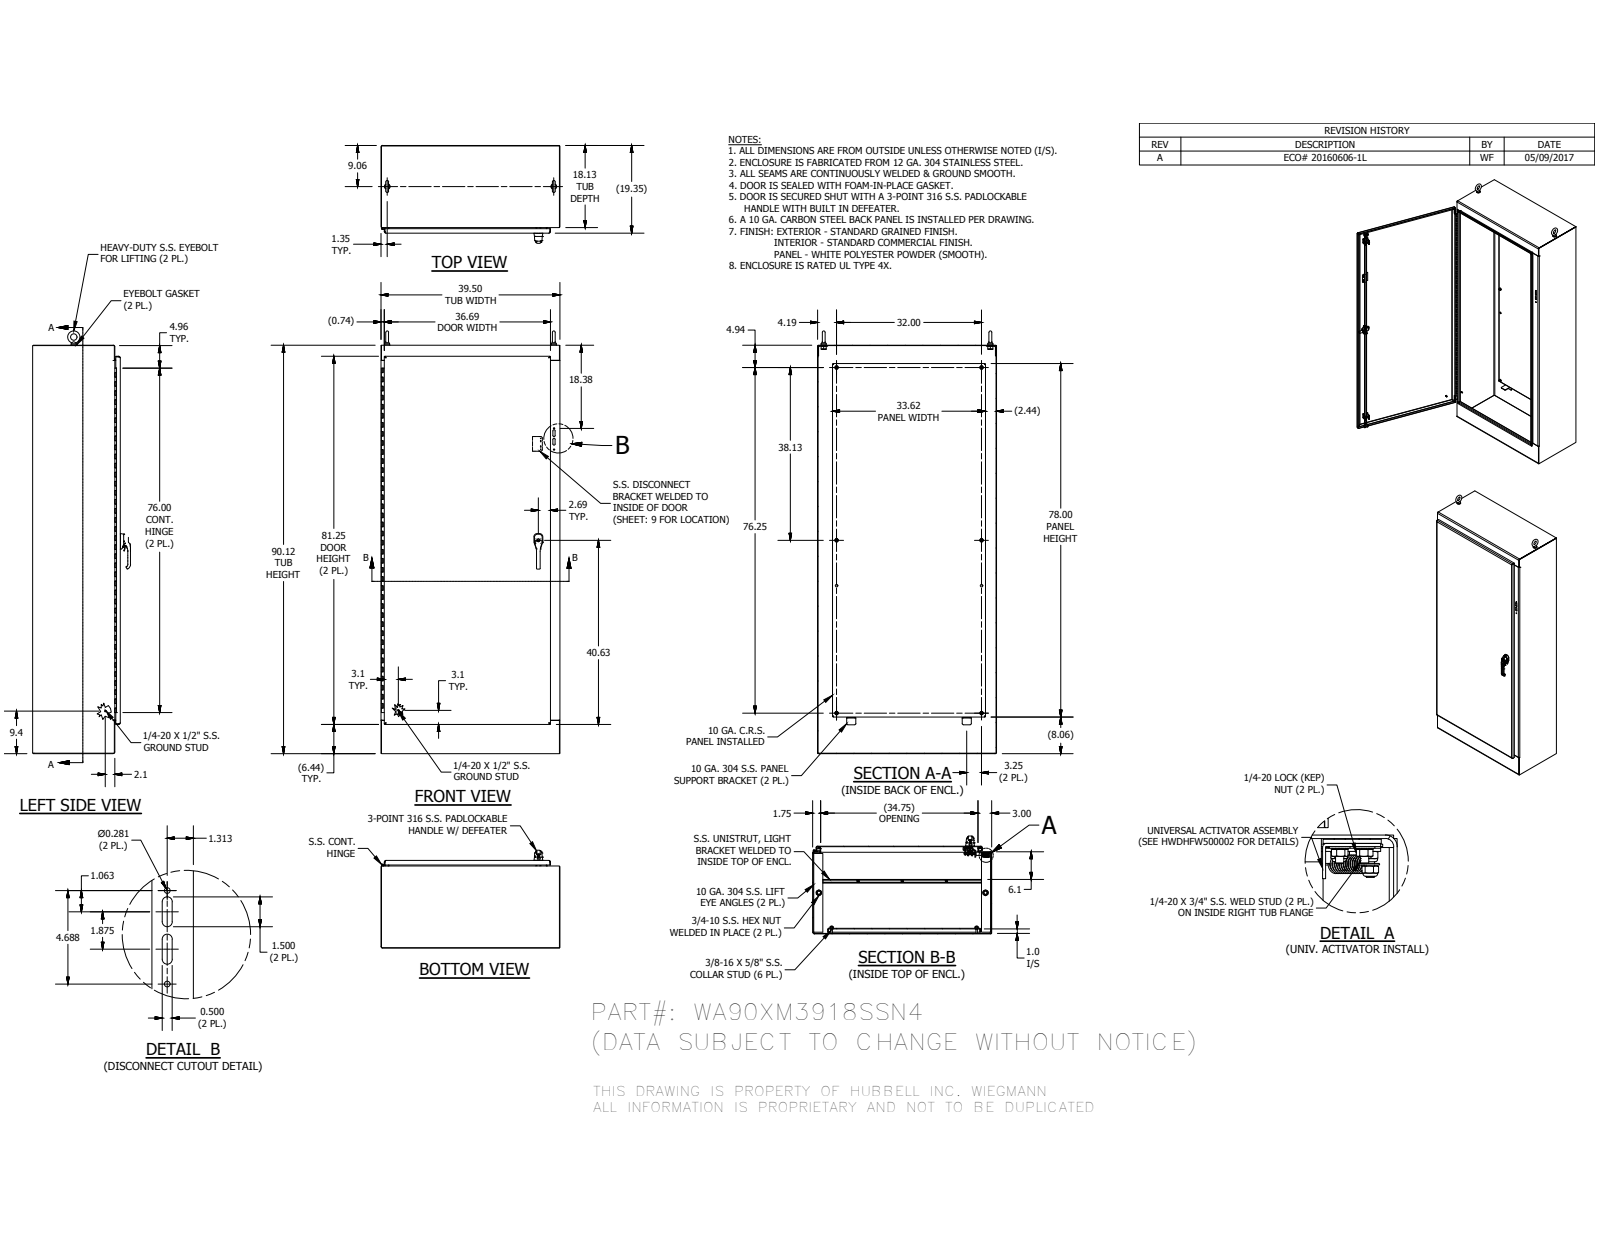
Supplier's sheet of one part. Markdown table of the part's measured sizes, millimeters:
| quantity | value |
| --- | --- |
| part name | WA90XM3918SSN4BLS; WAXM3918SSN4TOP; WAXM3918SSN4BTM; FUN00129_WAXM39SSN4 (+8 more) |
| STEP written by | Autodesk Inventor 2016 (AUTOMOTIVE_DESIGN) |
| units | millimeters |
| bodies | 127 solids, 4880 faces (2278 planar, 1560 cylindrical, 1042 other) |
| overall size | 2368.49 × 1003.3 × 548.55 |
| volume | 29 530 000 mm³ |
| surface area | 20 960 000 mm² |
| round holes (diameter × count) | 3.55 × 24, 9.52 × 10, 6.35 × 9, 6.65 × 8, 14.29 × 8, 3.96 × 6, 7.8 × 6, 4.76 × 5, 3.45 × 4, 4.17 × 4, 5.1 × 4, 7.37 × 4 |
| round bosses / shafts (diameter × count) | 15.88 × 10, 8.38 × 9, 14.29 × 6, 13.54 × 4, 8.56 × 4, 6.35 × 4, 6.02 × 4, 6 × 3 |
| partial cylindrical surfaces (radius × count) | 0.5 × 187, 0.3 × 109, 0.51 × 48, 6.35 × 25, 0.47 × 21, 1.59 × 20, 3.17 × 18, 0.64 × 16 |
| main face-to-face distances | 2.64, 488.79, 1000.66, 486.15, 491.43, 3.41, 25.4, 463.39, 31.45, 28.81 |
| hole center spacings | 0.45, 214.49, 0.6, 1830.75, 0.74, 9.65, 19.31, 428.98 |
